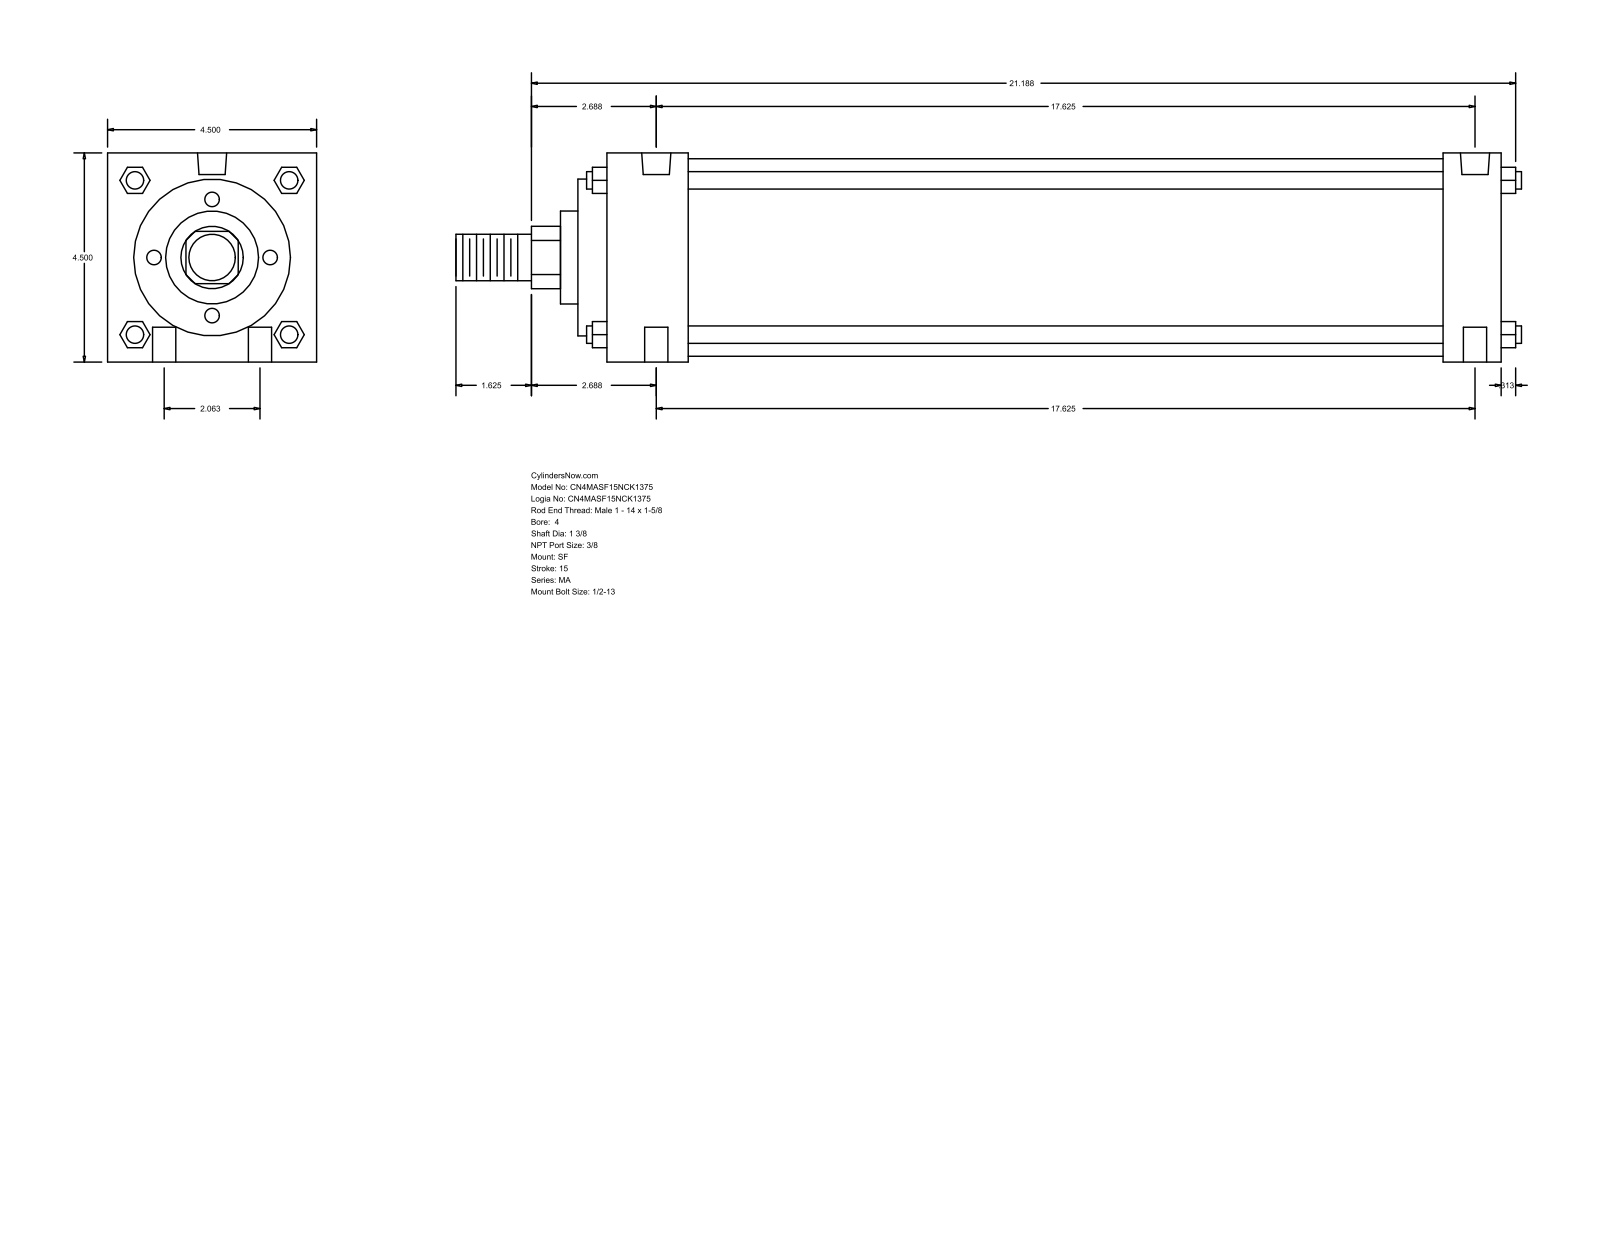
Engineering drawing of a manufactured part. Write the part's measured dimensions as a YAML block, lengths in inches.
part_name: "MA_SF__0400_1.375"
step_written_by: "GSSL Pune (CONFIG_CONTROL_DESIGN)"
units: inches
bodies: {solids: 0, faces: 126, planar: 95, cylindrical: 31, other: 0}
overall_size: [22.937, 4.5, 4.5]
round_holes:
  - {diameter: 0.5, count: 4}
  - {diameter: 0.437, count: 2}
  - {diameter: 0.627, count: 2}
round_bosses_or_shafts:
  - {diameter: 0.375, count: 4}
  - {diameter: 4.25, count: 1}
  - {diameter: 3.375, count: 1}
  - {diameter: 2, count: 1}
  - {diameter: 1.375, count: 1}
  - {diameter: 1, count: 1}
partial_cylinders:
  - {radius: 0.672, count: 1}
face_to_face_distances: [4.5, 19.25, 0.625, 19.875, 18.625, 18, 1.25, 2.375, 1.75, 16.25]
hole_center_spacings: [1.031, 17.656, 17.625, 2.062, 17.745, 17.25]
